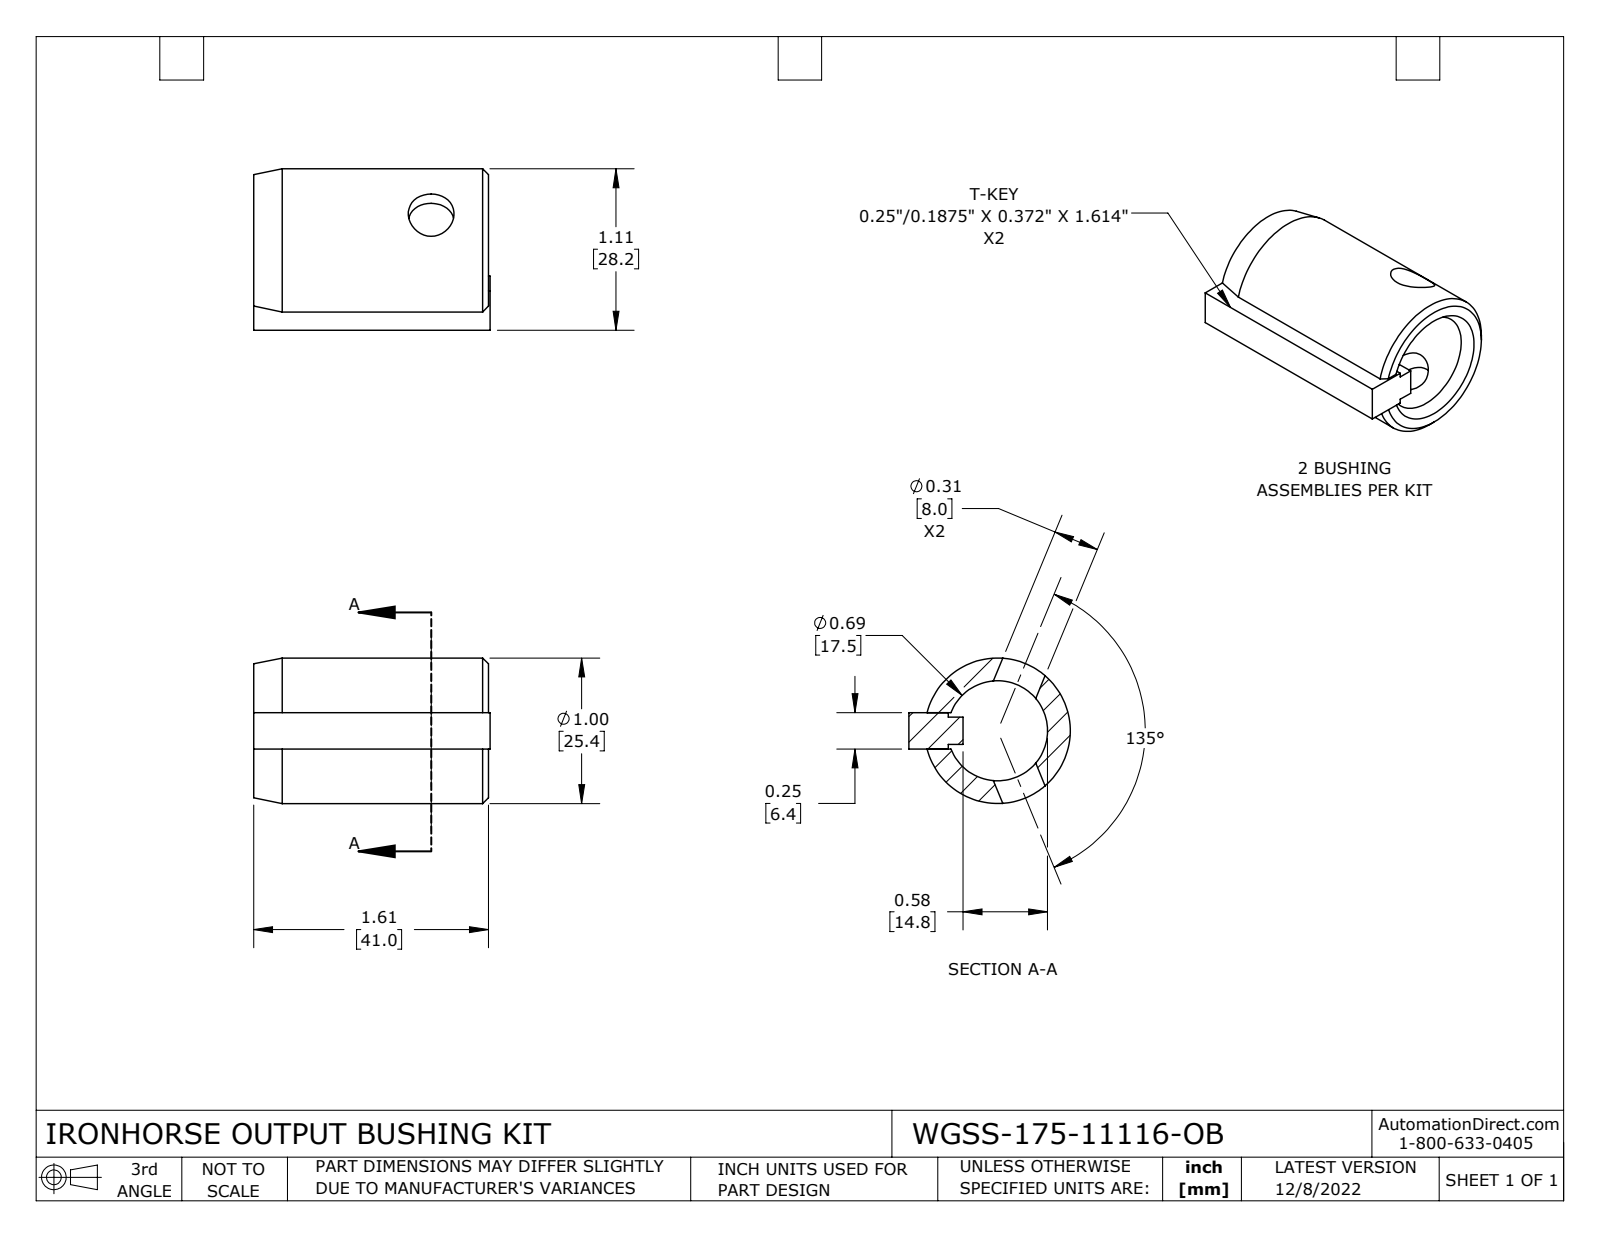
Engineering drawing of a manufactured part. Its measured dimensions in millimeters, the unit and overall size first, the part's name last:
Units: millimetres
Overall size (bounding box): 41.28 × 28.18 × 25.4
Round holes (diameter × count): ⌀8 ×2, ⌀17.46 ×1
Round bosses / shafts (diameter × count): ⌀25.4 ×1
Main face-to-face distances: 6.35, 9.45, 41, 0.8, 5.55, 5.56, 4.76, 0.79, 2.58, 6.87
Volume: 11 476 mm³ · Surface area: 7 027 mm²
Bodies: 2 solids, 35 faces (14 planar, 10 cylindrical, 11 other)
Part name (STEP PRODUCT): WGSS-175-11116-OB
STEP written by: SolidWorks 2021 (CONFIG_CONTROL_DESIGN)
